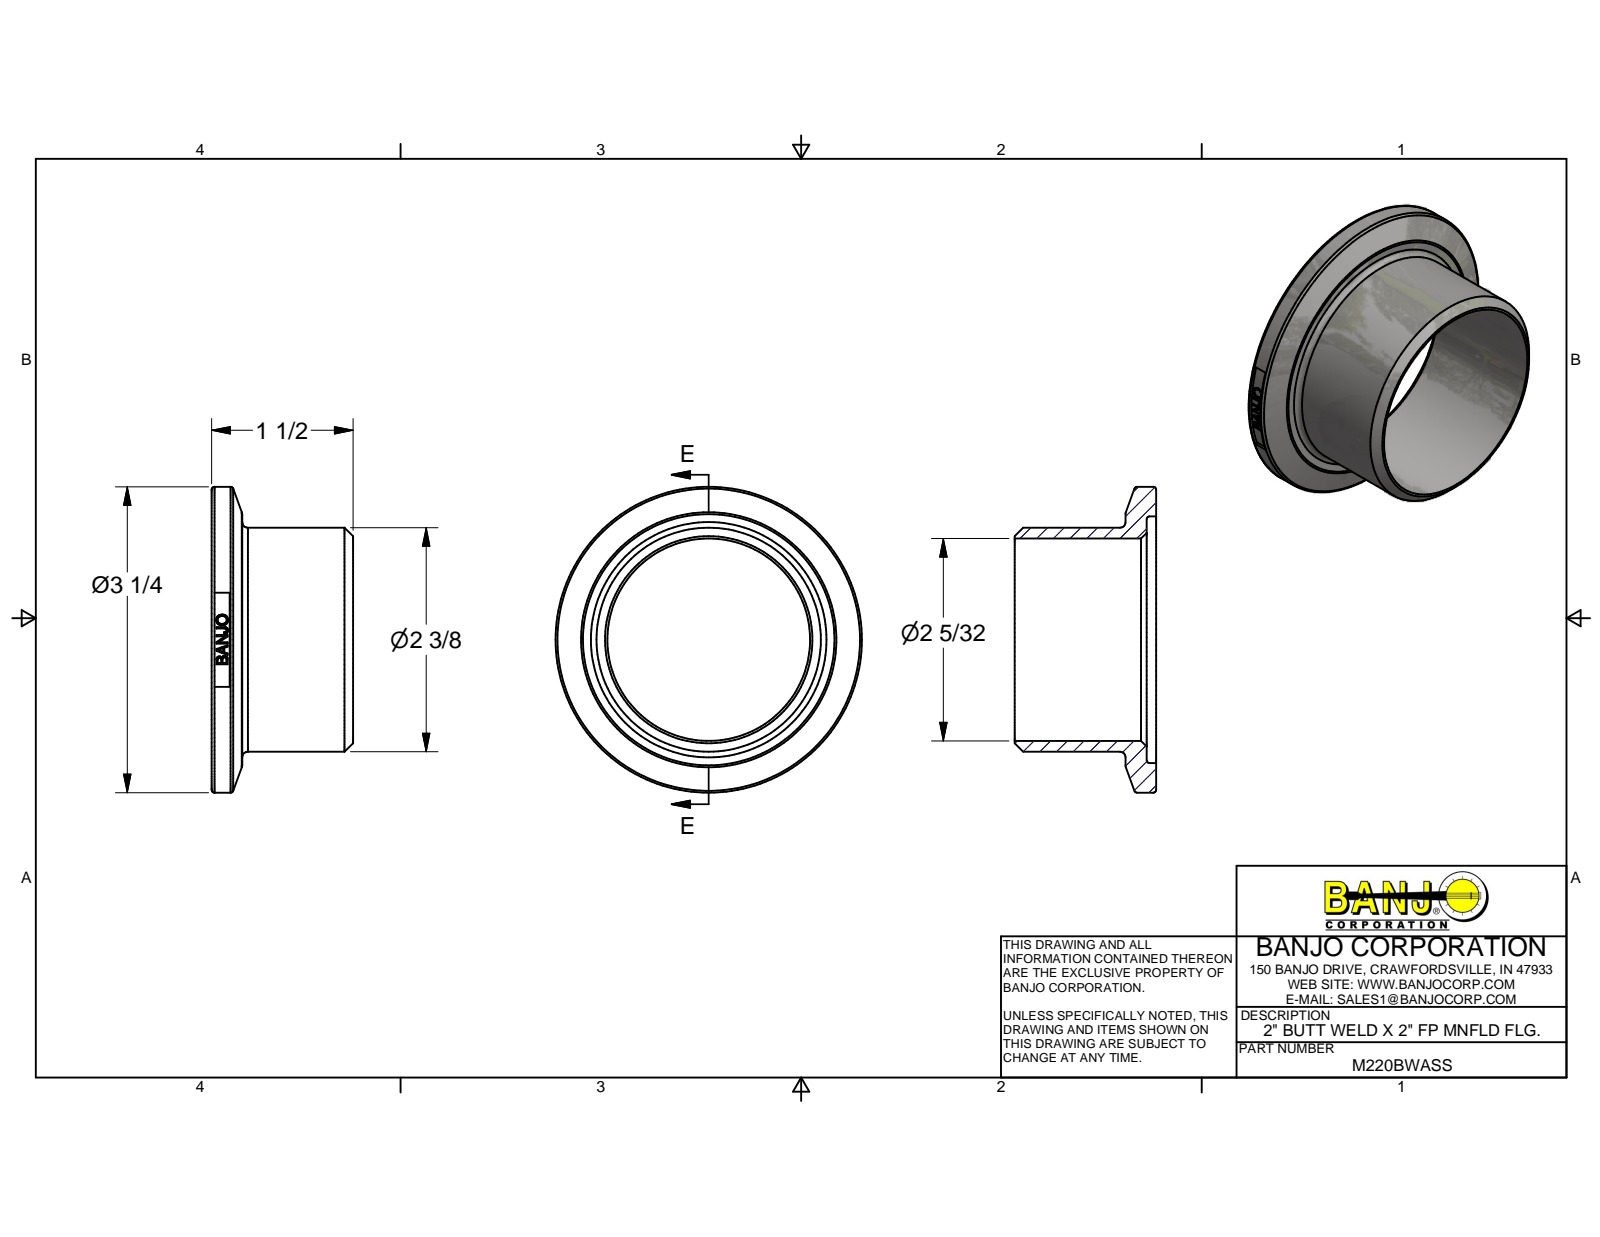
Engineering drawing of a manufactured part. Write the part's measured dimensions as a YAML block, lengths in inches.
part_name: "M220BWASS"
step_written_by: "Autodesk Inventor 2016 (AUTOMOTIVE_DESIGN)"
units: inches
bodies: {solids: 1, faces: 261, planar: 115, cylindrical: 28, other: 118}
overall_size: [3.25, 3.25, 1.5]
volume: 2.111
surface_area: 30.13
round_holes:
  - {diameter: 2.15, count: 1}
  - {diameter: 2.62, count: 1}
round_bosses_or_shafts:
  - {diameter: 3.25, count: 1}
  - {diameter: 2.38, count: 1}
partial_cylinders:
  - {radius: 1.565, count: 1}
  - {radius: 1.595, count: 1}
face_to_face_distances: [0.1, 0.224, 0.324, 1.176, 1.4, 1.5, 0.07, 0.092, 1.308, 0.132]
